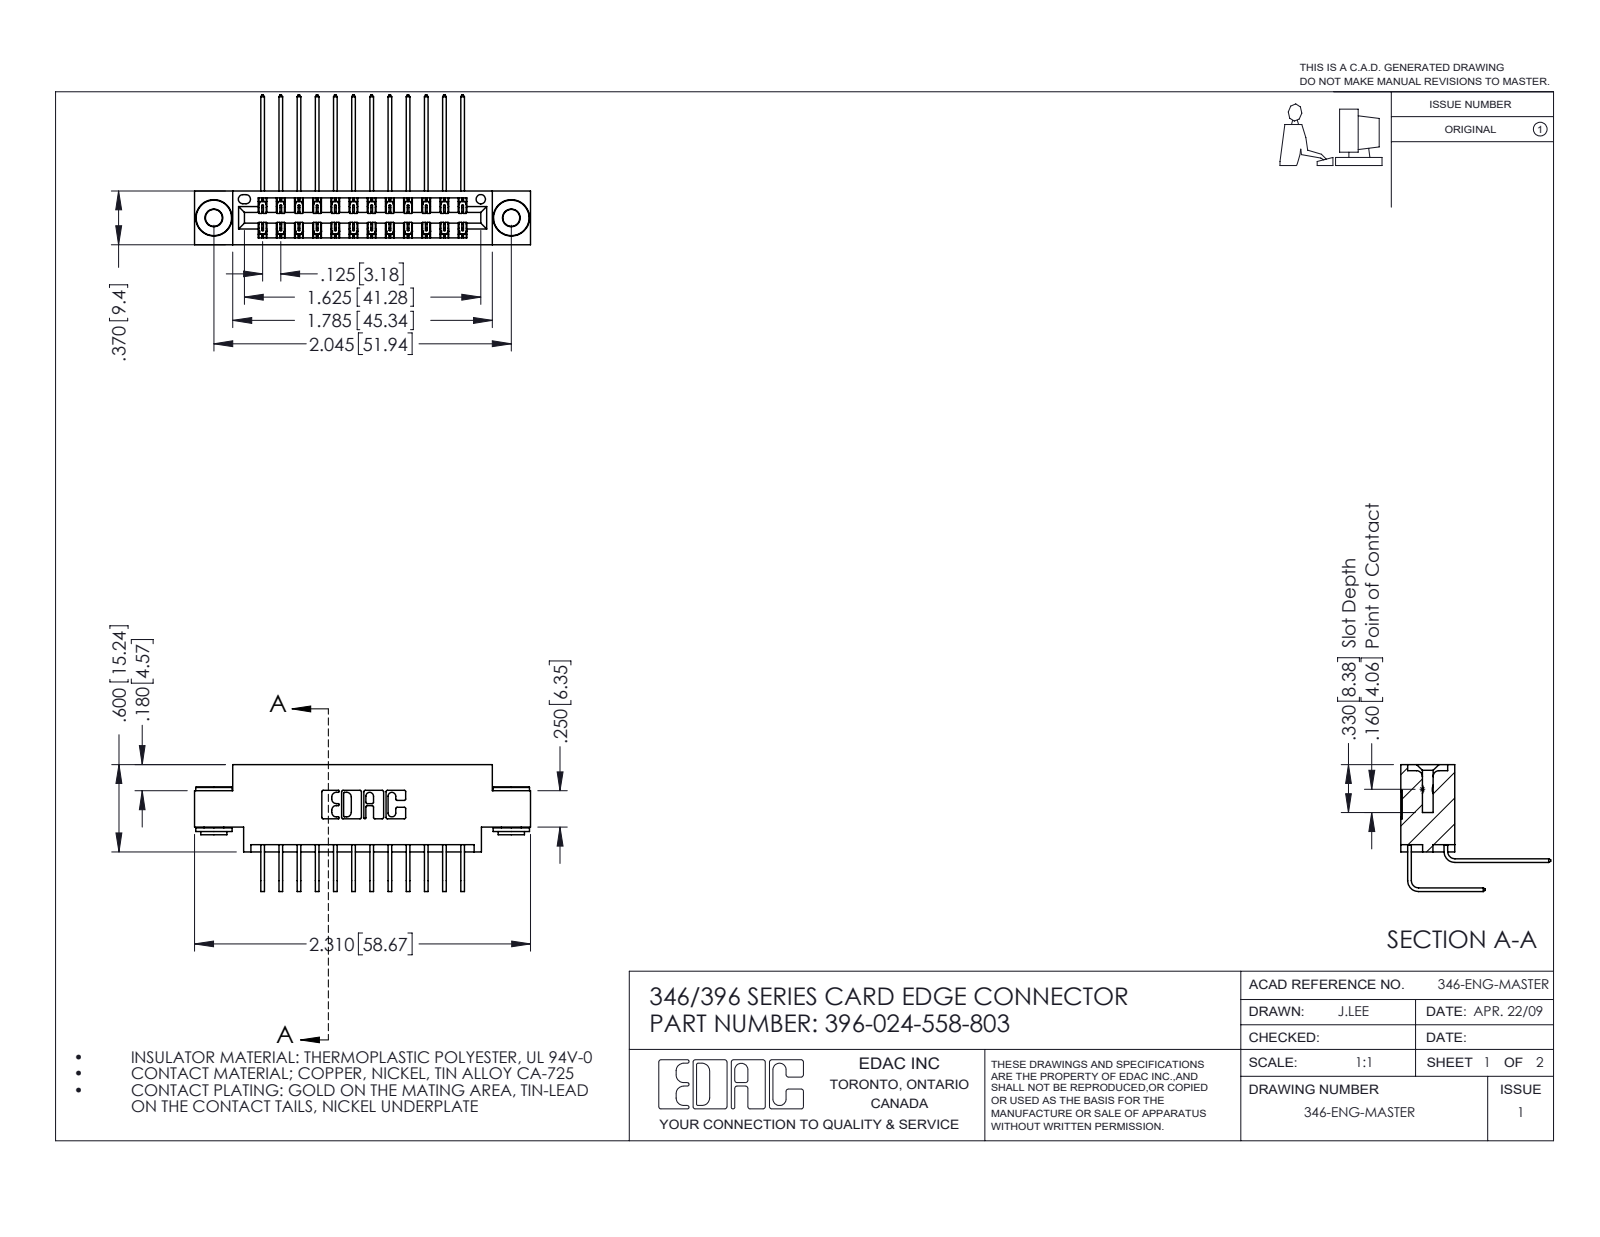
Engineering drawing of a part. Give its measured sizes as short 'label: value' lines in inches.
name: 345-292-001_558 559 Tail - 1; 346 Part_0.170 Offset - 0.156 Dia-TH; 396-024-558-803; 345-292-001_558 Tail - 2 (+1 more)
written by: SolidWorks 2016 (CONFIG_CONTROL_DESIGN)
unit: in
bodies: 27 solids, 1460 faces (978 planar, 474 cylindrical, 8 other)
size: 2.31 × 1.03 × 0.873
volume: 0.335 in³; area: 12.61 in²
holes: 2× ⌀0.116, 2× ⌀0.156, 1× ⌀0.064
bosses: 2× ⌀0.25, 2× ⌀0.18, 2× ⌀0.136
rounds: 36× R0.006, 22× R0.01, 6× R0.007, 6× R0.031, 3× R0.026, 2× R0.014, 2× R0.022, 2× R0.024
face distances: 0.048, 0.322, 0.25, 0.37, 0.025, 0.072, 0.298, 0.275, 0.148, 0.222
hole spacings: 0.246, 1.839, 2.045
